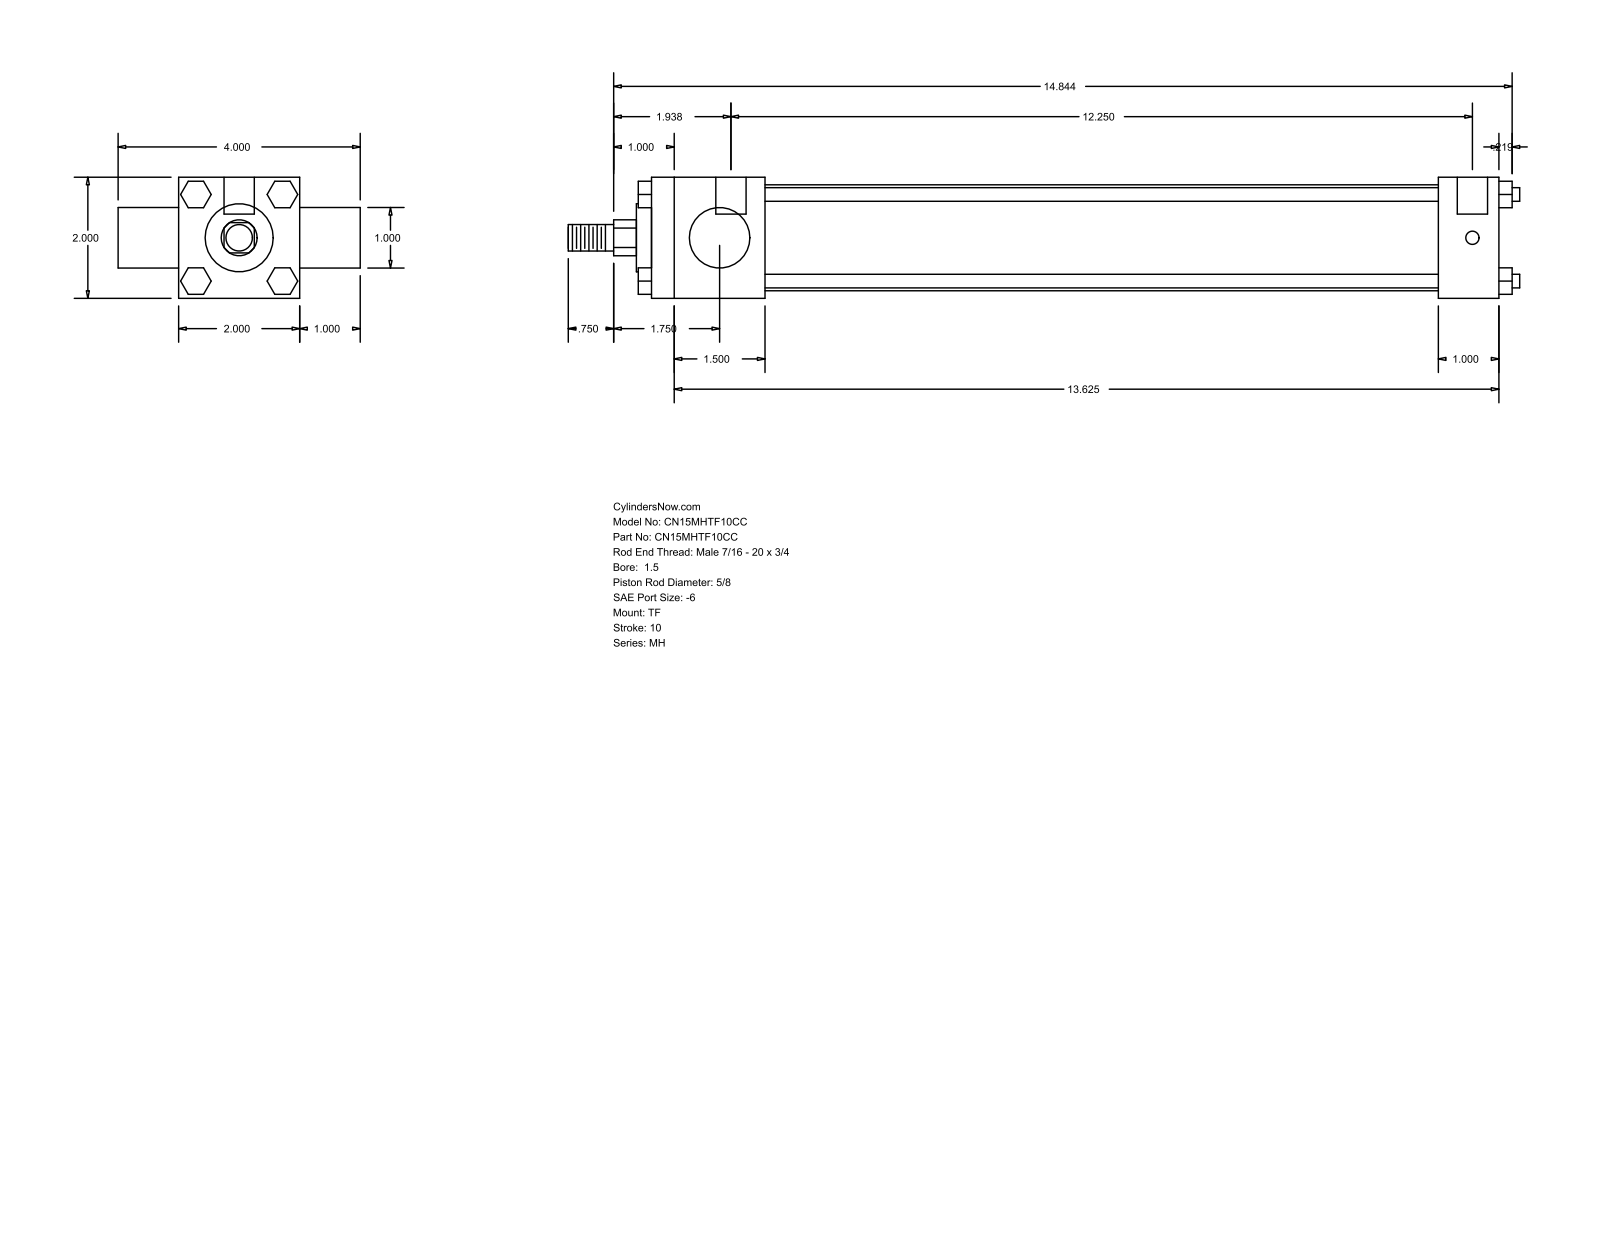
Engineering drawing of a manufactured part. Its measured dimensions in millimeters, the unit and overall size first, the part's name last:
Units: millimetres
Overall size (bounding box): 399.26 × 101.6 × 50.8
Round holes (diameter × count): ⌀5.56 ×3, ⌀12.7 ×2
Round bosses / shafts (diameter × count): ⌀5.71 ×4, ⌀44.45 ×1, ⌀28.57 ×1, ⌀25.4 ×1, ⌀15.88 ×1, ⌀11.11 ×1
Partial cylindrical surfaces — rounded edges, fillets, slot ends (radius × count): R7.54 ×1
Main face-to-face distances: 50.8, 355.6, 25.4, 76.2, 47.62, 307.98, 330.19, 282.57, 25.41, 11.11
Hole centre spacings: 3.17, 311.15, 314.32
Bodies: 0 solids, 120 faces (92 planar, 28 cylindrical, 0 other)
Part name (STEP PRODUCT): MH_TF__0150_0.625
STEP written by: GSSL Pune (CONFIG_CONTROL_DESIGN)
